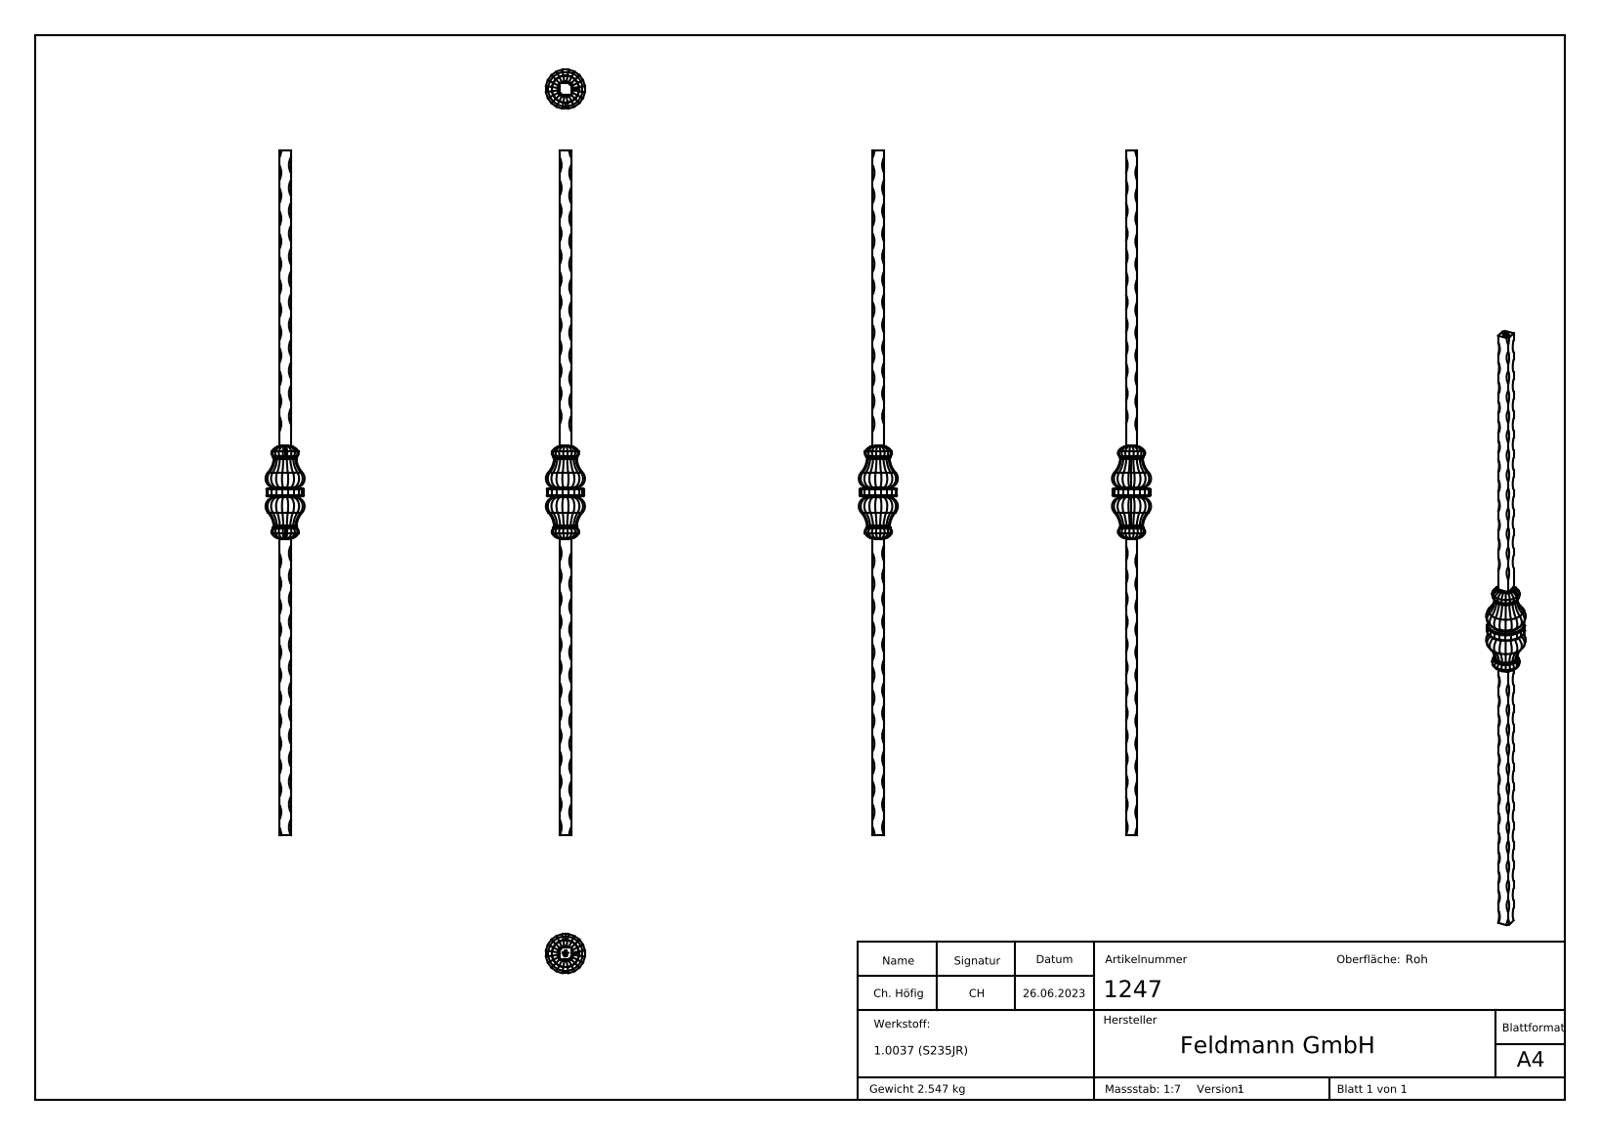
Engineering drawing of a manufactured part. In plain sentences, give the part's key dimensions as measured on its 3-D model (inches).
The part is named "1266". Its 3-D file was written by "SolidWorks 2018 (CONFIG_CONTROL_DESIGN)". It is 1 solid with 818 faces: 170 planar, 422 cylindrical and 226 other. Overall it measures 35.433 by 2.023 by 2.023 inches. Its volume is 19.93 cubic inches and its surface area 102.9 square inches. Partial cylindrical surfaces (rounded edges, fillets, slot ends): 120 of radius 0.02, 48 of radius 0.047, 40 of radius 0.059, 40 of radius 0.118, 40 of radius 0.197, 40 of radius 0.445, 40 of radius 0.474, 40 of radius 1.181. The main face-to-face distances are 0.591, 0.413, 0.039, 0.453, 1.944, 17.47, 17.51, 17.923, 17.963, 0.492.
